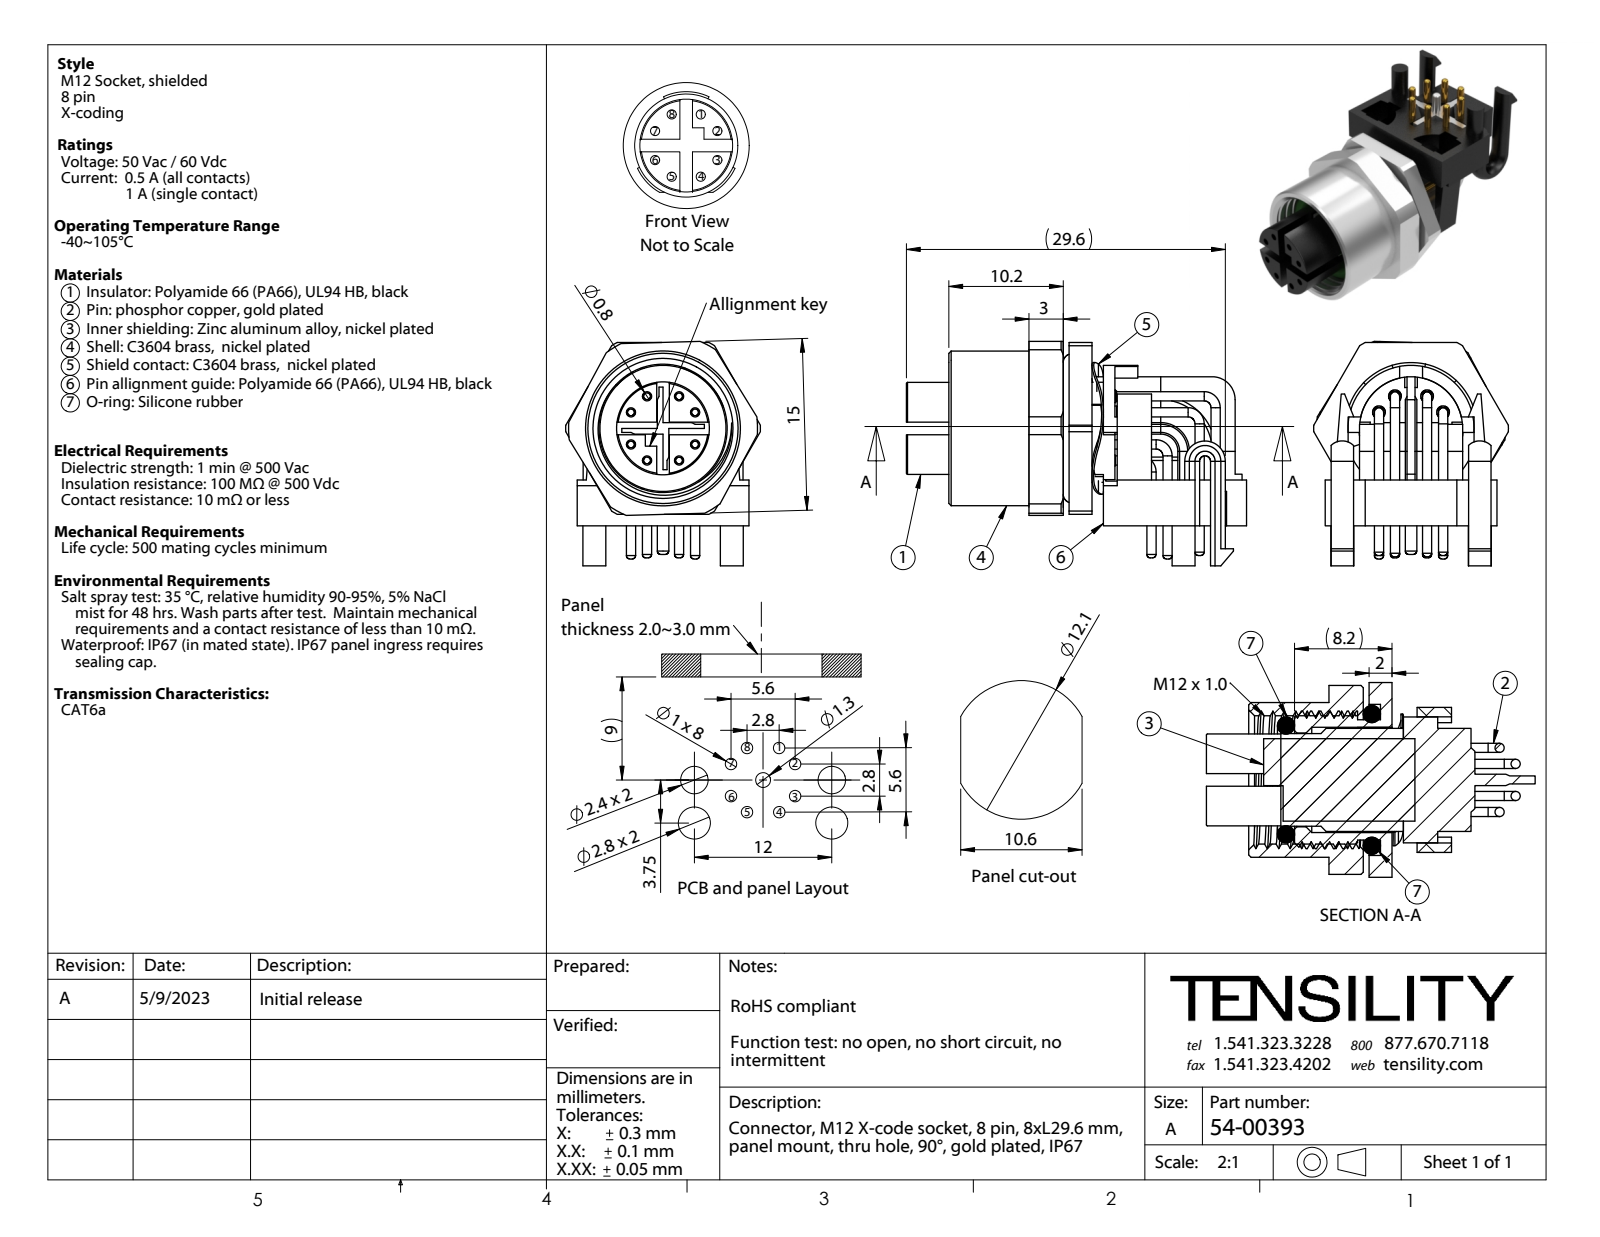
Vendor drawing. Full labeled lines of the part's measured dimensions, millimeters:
Part name (STEP PRODUCT): 54-00393-09; 54-00393; 54-00393-05; 54-00393-02 (+8 more)
STEP written by: SolidWorks 2021 (CONFIG_CONTROL_DESIGN)
Units: millimetres
Bodies: 16 solids, 829 faces (366 planar, 267 cylindrical, 196 other)
Overall size (bounding box): 29.7 × 19.59 × 17
Volume: 2 989 mm³ · Surface area: 6 761 mm²
Round holes (diameter × count): ⌀0.8 ×16, ⌀0.6 ×8, ⌀8.2 ×1, ⌀9 ×1, ⌀9.1 ×1, ⌀9.2 ×1, ⌀11.2 ×1, ⌀13.2 ×1
Round bosses / shafts (diameter × count): ⌀1.1 ×8, ⌀2 ×2, ⌀13.5 ×1, ⌀11.5 ×1, ⌀10.5 ×1, ⌀8.1 ×1, ⌀1 ×1
Partial cylindrical surfaces — rounded edges, fillets, slot ends (radius × count): R1.4 ×8, R0.2 ×2, R0.5 ×2, R3.52 ×2, R1.5 ×1, R1.65 ×1, R2 ×1, R2.35 ×1
Main face-to-face distances: 1, 4, 2, 3, 0.85, 7.5, 3.5, 5, 4.5, 6.5
Hole centre spacings: 4.43, 1.98, 2.8, 3.13, 5.6, 5.94, 6.26
